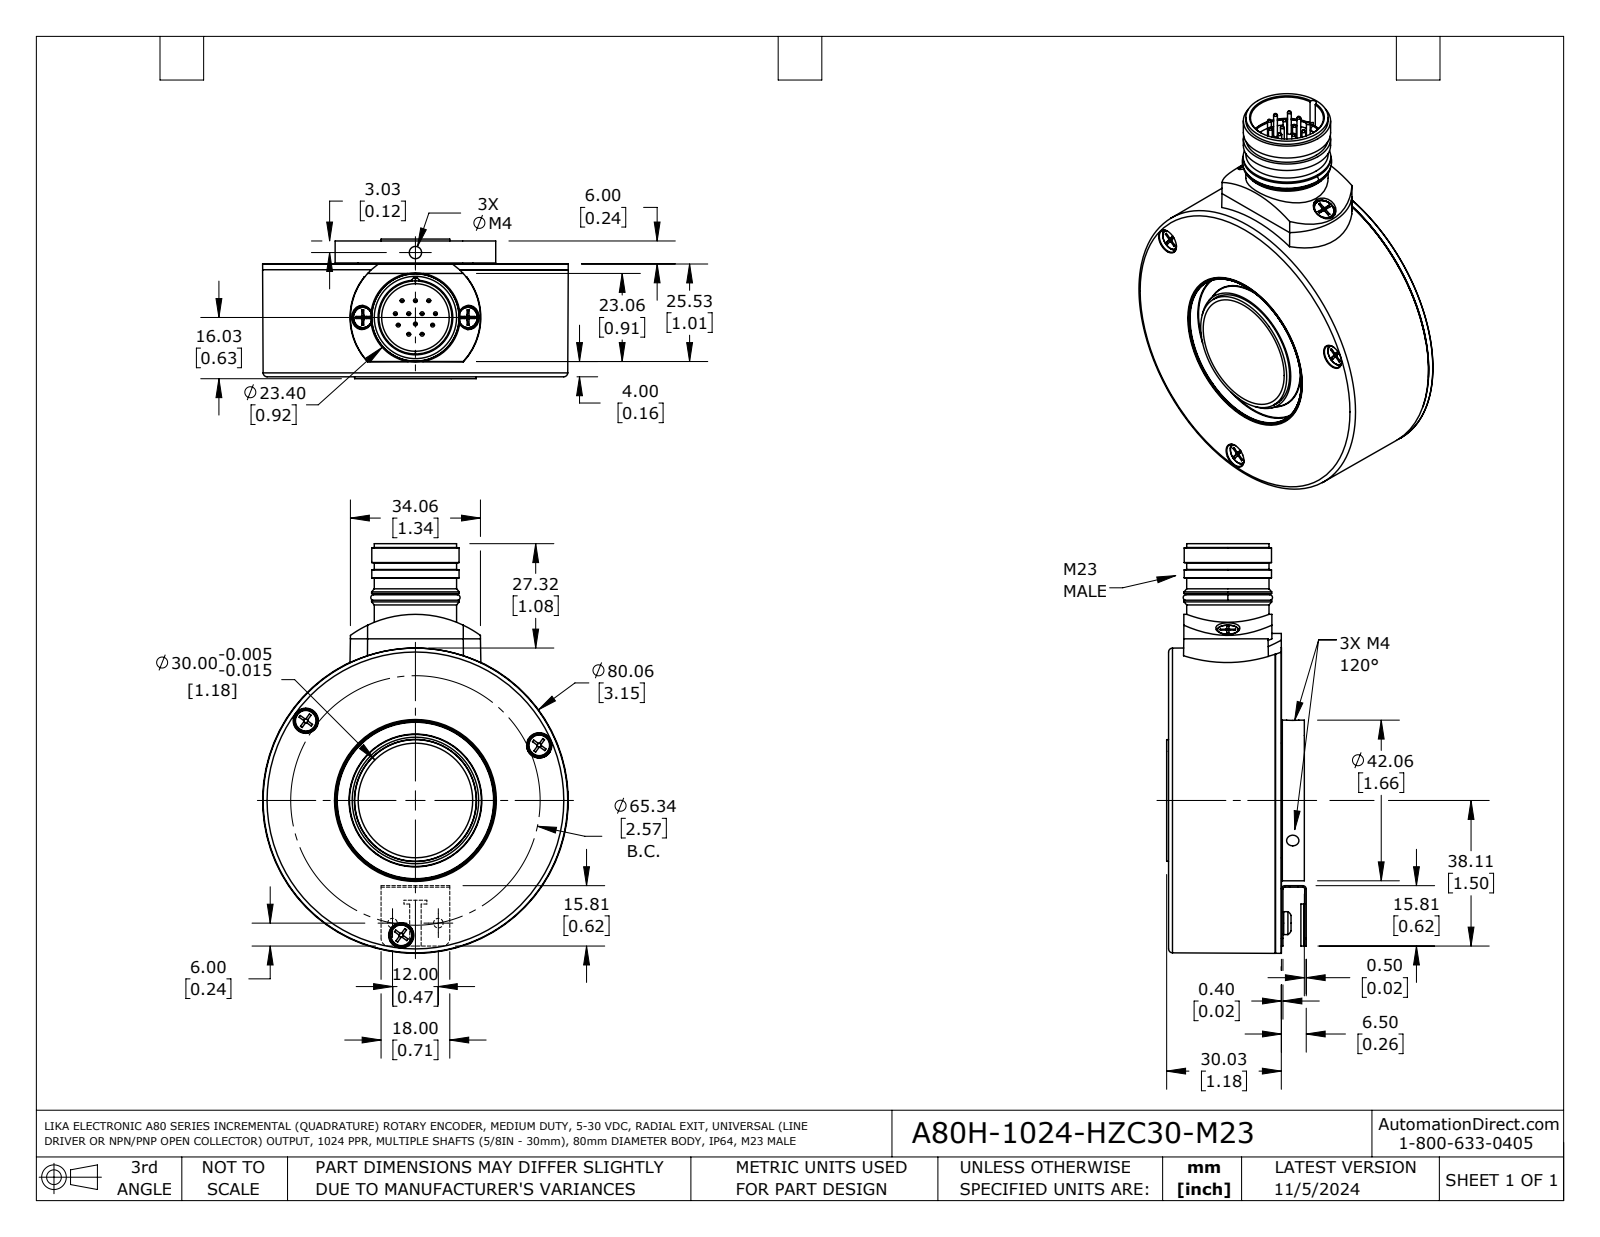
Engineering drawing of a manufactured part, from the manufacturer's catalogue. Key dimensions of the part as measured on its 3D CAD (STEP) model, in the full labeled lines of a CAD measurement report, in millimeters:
Part name (STEP PRODUCT): A80H-1024-HZC30-M23
STEP written by: SolidWorks 2021 (AUTOMOTIVE_DESIGN)
Units: millimetres
Bodies: 12 solids, 962 faces (295 planar, 313 cylindrical, 354 other)
Overall size (bounding box): 107.3 × 80.1 × 36.6
Volume: 10 500 mm³ · Surface area: 59 860 mm²
Round holes (diameter × count): ⌀0.9 ×12, ⌀6.4 ×5, ⌀3.3 ×3, ⌀6.6 ×3, ⌀2.7 ×2, ⌀3.1 ×2, ⌀3.4 ×2, ⌀4 ×2, ⌀19.2 ×1, ⌀20.7 ×1, ⌀21.4 ×1, ⌀22.7 ×1
Round bosses / shafts (diameter × count): ⌀1 ×12, ⌀6.5 ×5, ⌀3.4 ×3, ⌀6 ×2, ⌀3 ×2, ⌀80.1 ×1, ⌀77.7 ×1, ⌀44 ×1
Partial cylindrical surfaces — rounded edges, fillets, slot ends (radius × count): R0.2 ×15, R0.2 ×15, R0.3 ×14, R0.4 ×12, R0.2 ×5, R0.2 ×5, R0.5 ×2, R0.7 ×2
Main face-to-face distances: 29.3, 29.4, 29.6, 29.5, 6, 6.2, 0.5, 5.7, 35.3, 32.3
Hole centre spacings: 3.5, 3.8, 3.2, 6.2, 6.5, 9, 7, 35.5
